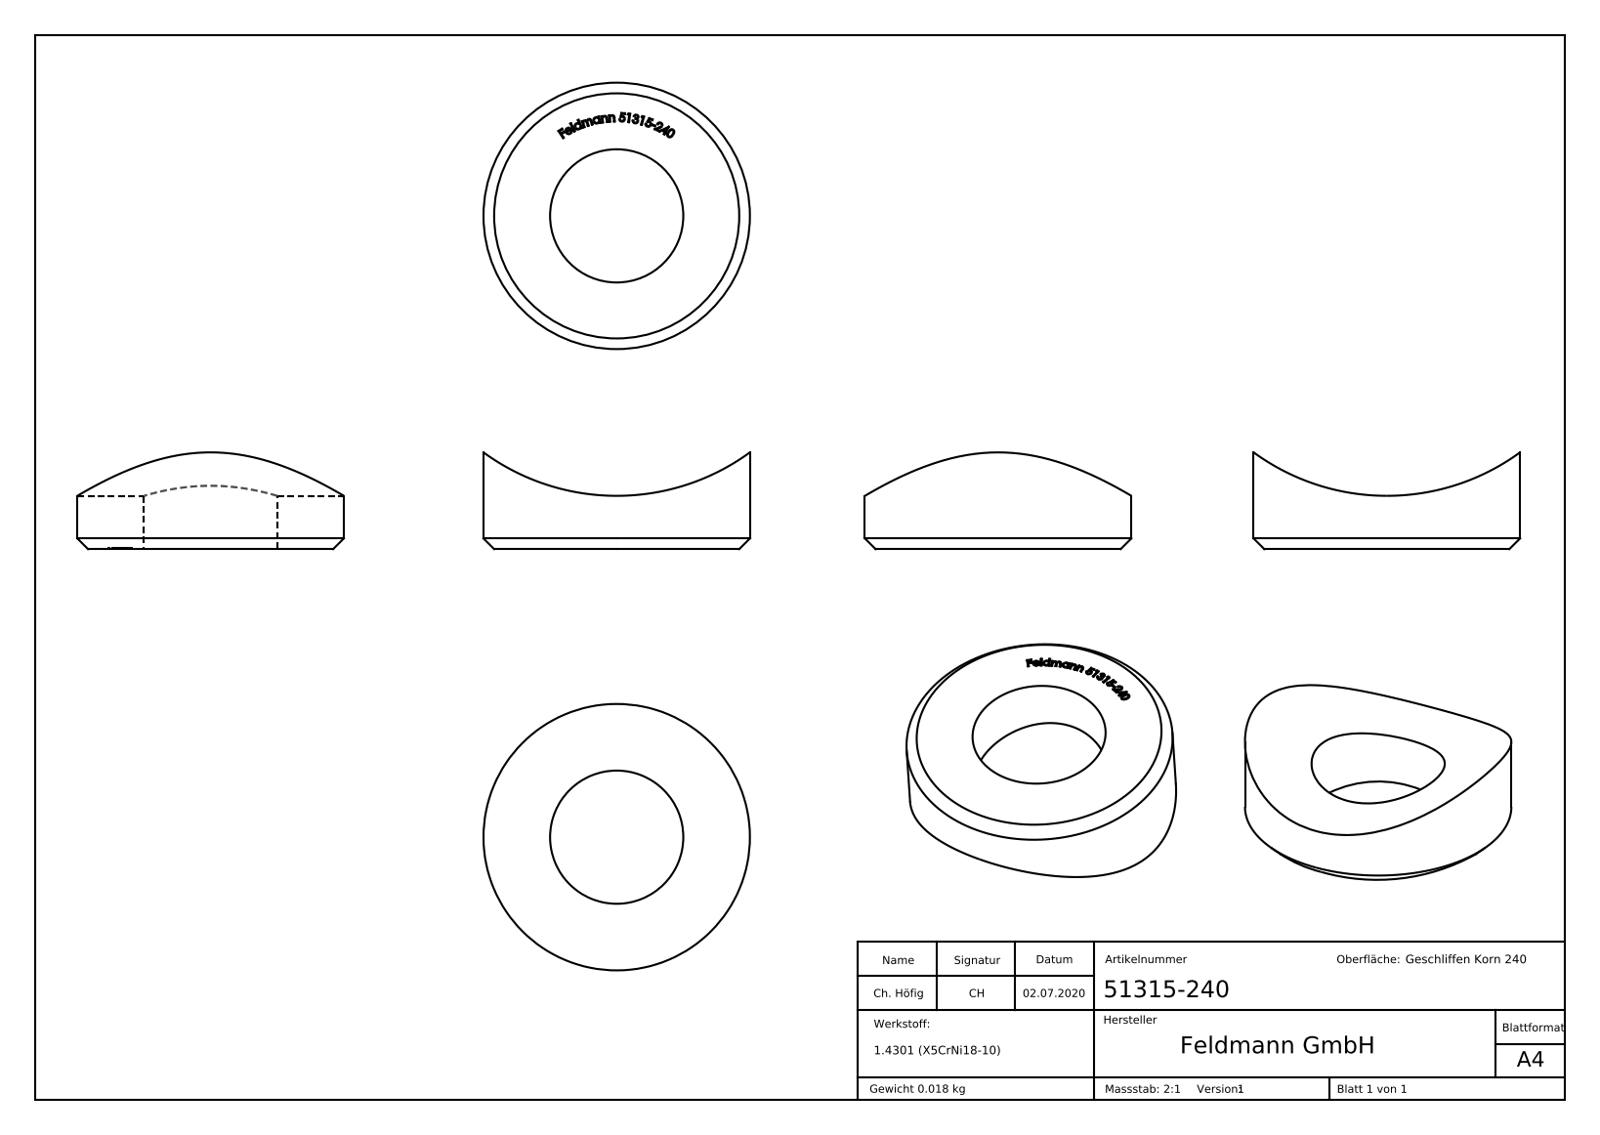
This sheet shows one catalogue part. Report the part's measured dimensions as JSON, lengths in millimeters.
{"part_name": "51315-240", "step_written_by": "SolidWorks 2018 (CONFIG_CONTROL_DESIGN)", "units": "millimeters", "bodies": {"solids": 1, "faces": 227, "planar": 127, "cylindrical": 5, "other": 95}, "overall_size": [25, 25, 9.08], "volume_mm3": 2248, "surface_area_mm2": 1481, "round_holes": [[12.5, 1]], "round_bosses_or_shafts": [[25, 1]], "partial_cylinders_radius": [[21.2, 1]], "face_to_face_distances": [0.4, 0.32, 0.47, 0.51, 0.79, 0.44, 0.36, 0.8, 0.87, 0.39]}
